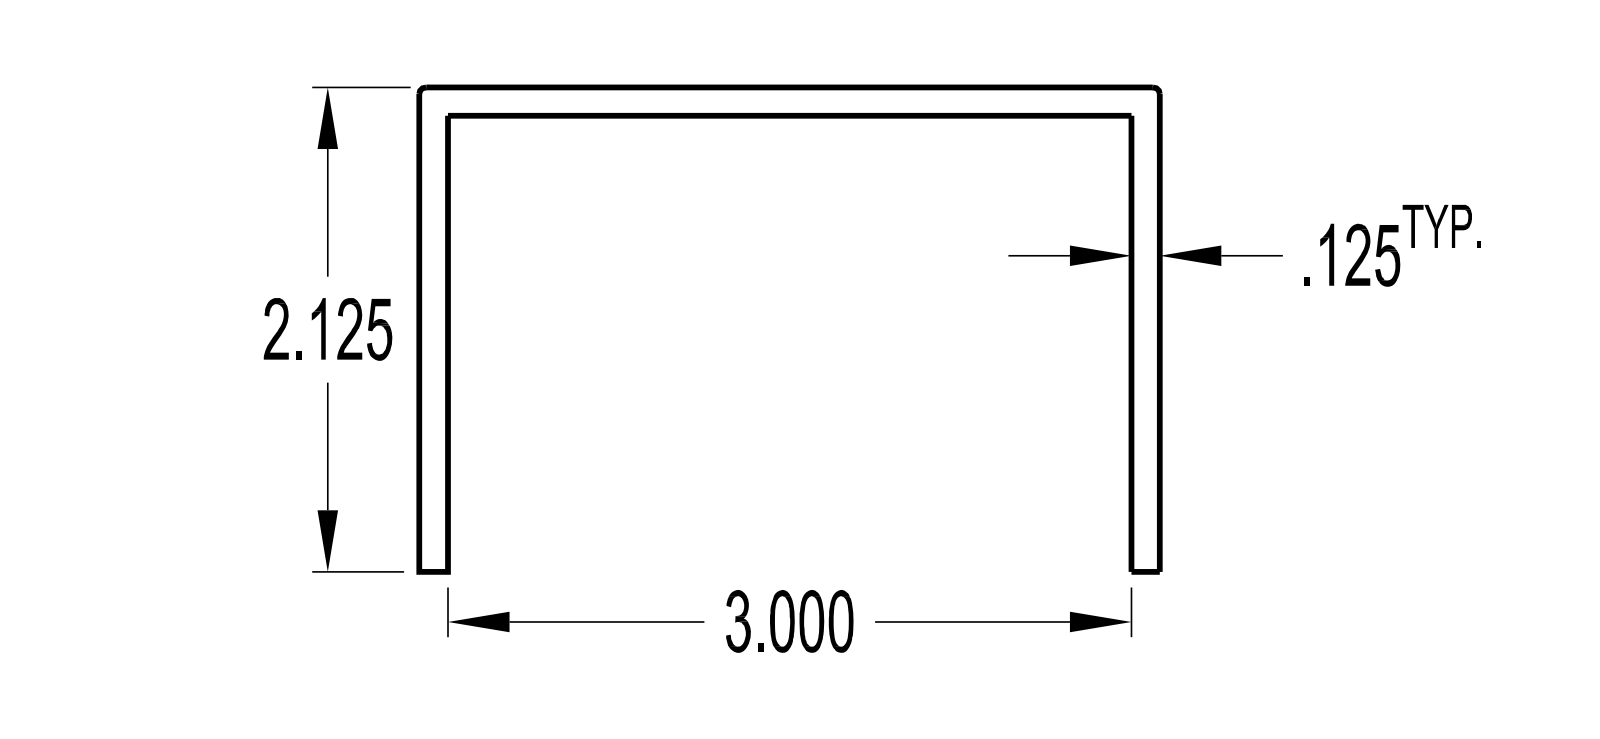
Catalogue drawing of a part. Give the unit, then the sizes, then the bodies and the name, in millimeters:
Units: millimetres
Overall size (bounding box): 152.4 × 82.6 × 54
Partial cylindrical surfaces — rounded edges, fillets, slot ends (radius × count): R0.8 ×2
Main face-to-face distances: 3.2, 82.6, 79.4, 76.2, 79.4, 3.2, 50.8, 54, 152.4
Volume: 89 060 mm³ · Surface area: 58 170 mm²
Bodies: 1 solid, 12 faces (10 planar, 2 cylindrical, 0 other)
STEP written by: KeyCreator Pro (AUTOMOTIVE_DESIGN)
